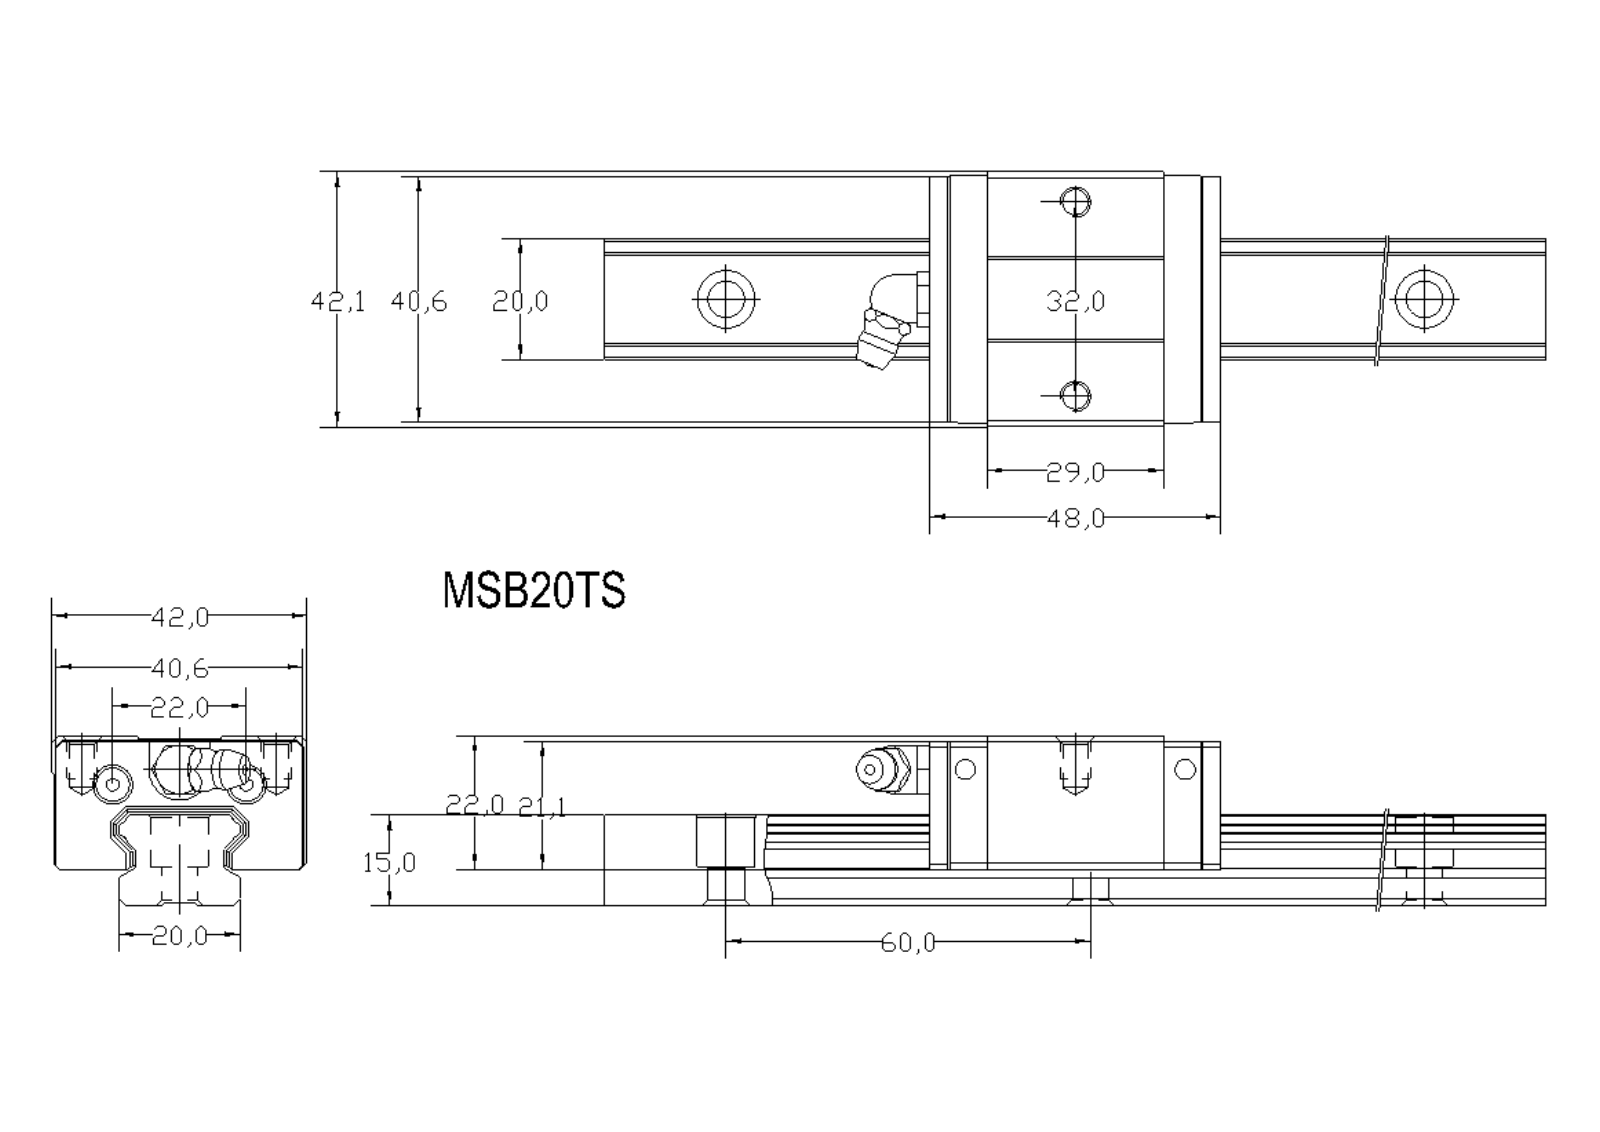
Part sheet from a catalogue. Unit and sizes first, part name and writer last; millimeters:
Units: millimetres
Overall size (bounding box): 220 × 42 × 28
Round holes (diameter × count): ⌀6 ×4, ⌀9.5 ×4, ⌀6.5 ×3, ⌀5 ×2
Round bosses / shafts (diameter × count): ⌀8 ×1
Partial cylindrical surfaces — rounded edges, fillets, slot ends (radius × count): R1.8 ×4, R0.7 ×2, R5.05 ×1
Main face-to-face distances: 15, 2.7, 17.3, 13, 9, 6, 0.6, 5.4, 14.4, 14.6
Hole centre spacings: 34, 91.41, 60, 11.28, 120, 22, 32, 180
Volume: 88 249 mm³ · Surface area: 28 245 mm²
Bodies: 3 solids, 184 faces (115 planar, 48 cylindrical, 21 other)
STEP written by: Kubotek KeyCreator V6.5.2 (0407) (CONFIG_CONTROL_DESIGN)
